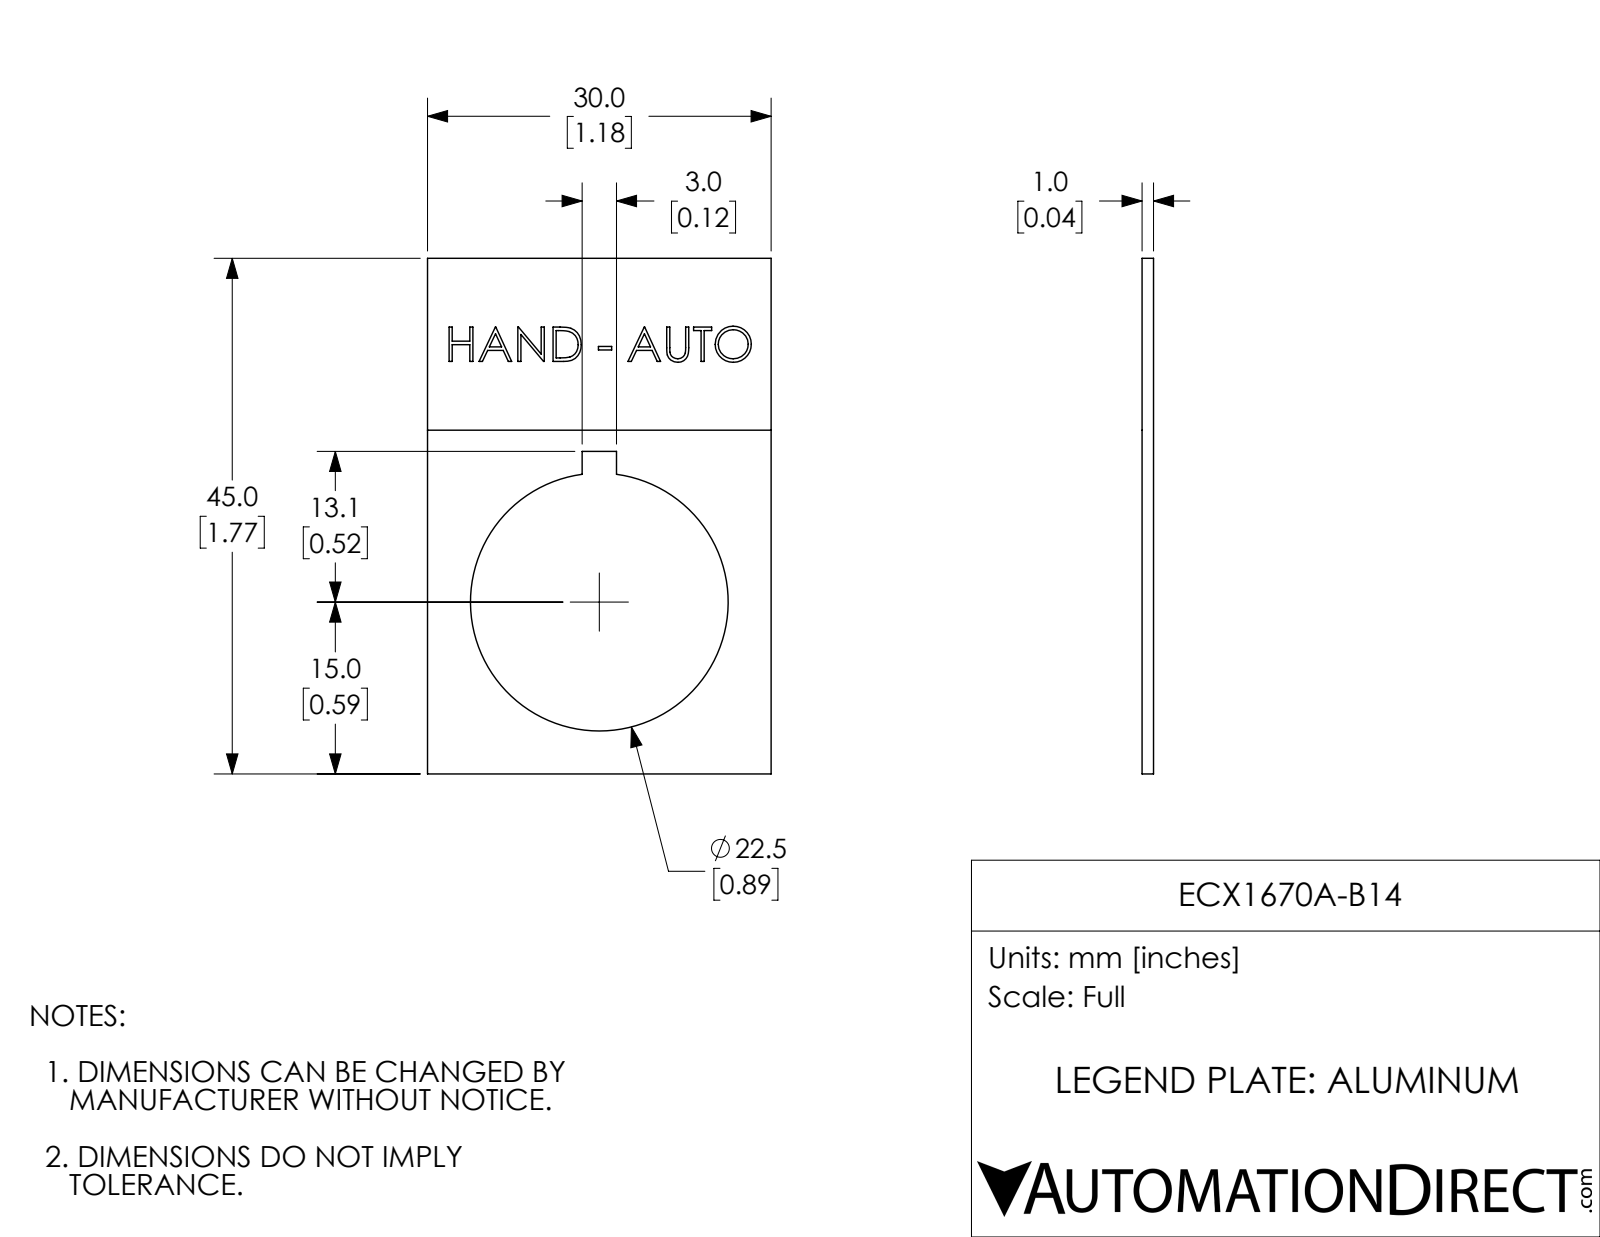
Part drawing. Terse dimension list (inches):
name: ECX1670A-B14
written by: SolidWorks 2017 (AUTOMOTIVE_DESIGN)
unit: in
bodies: 1 solid, 116 faces (91 planar, 3 cylindrical, 22 other)
size: 1.772 × 1.181 × 0.039
volume: 0.058 in³; area: 3.288 in²
holes: 1× ⌀0.886
face distances: 0.039, 1.181, 1.772, 0.038, 0.531, 0.65, 1.108, 0.663, 0.118, 0.236
